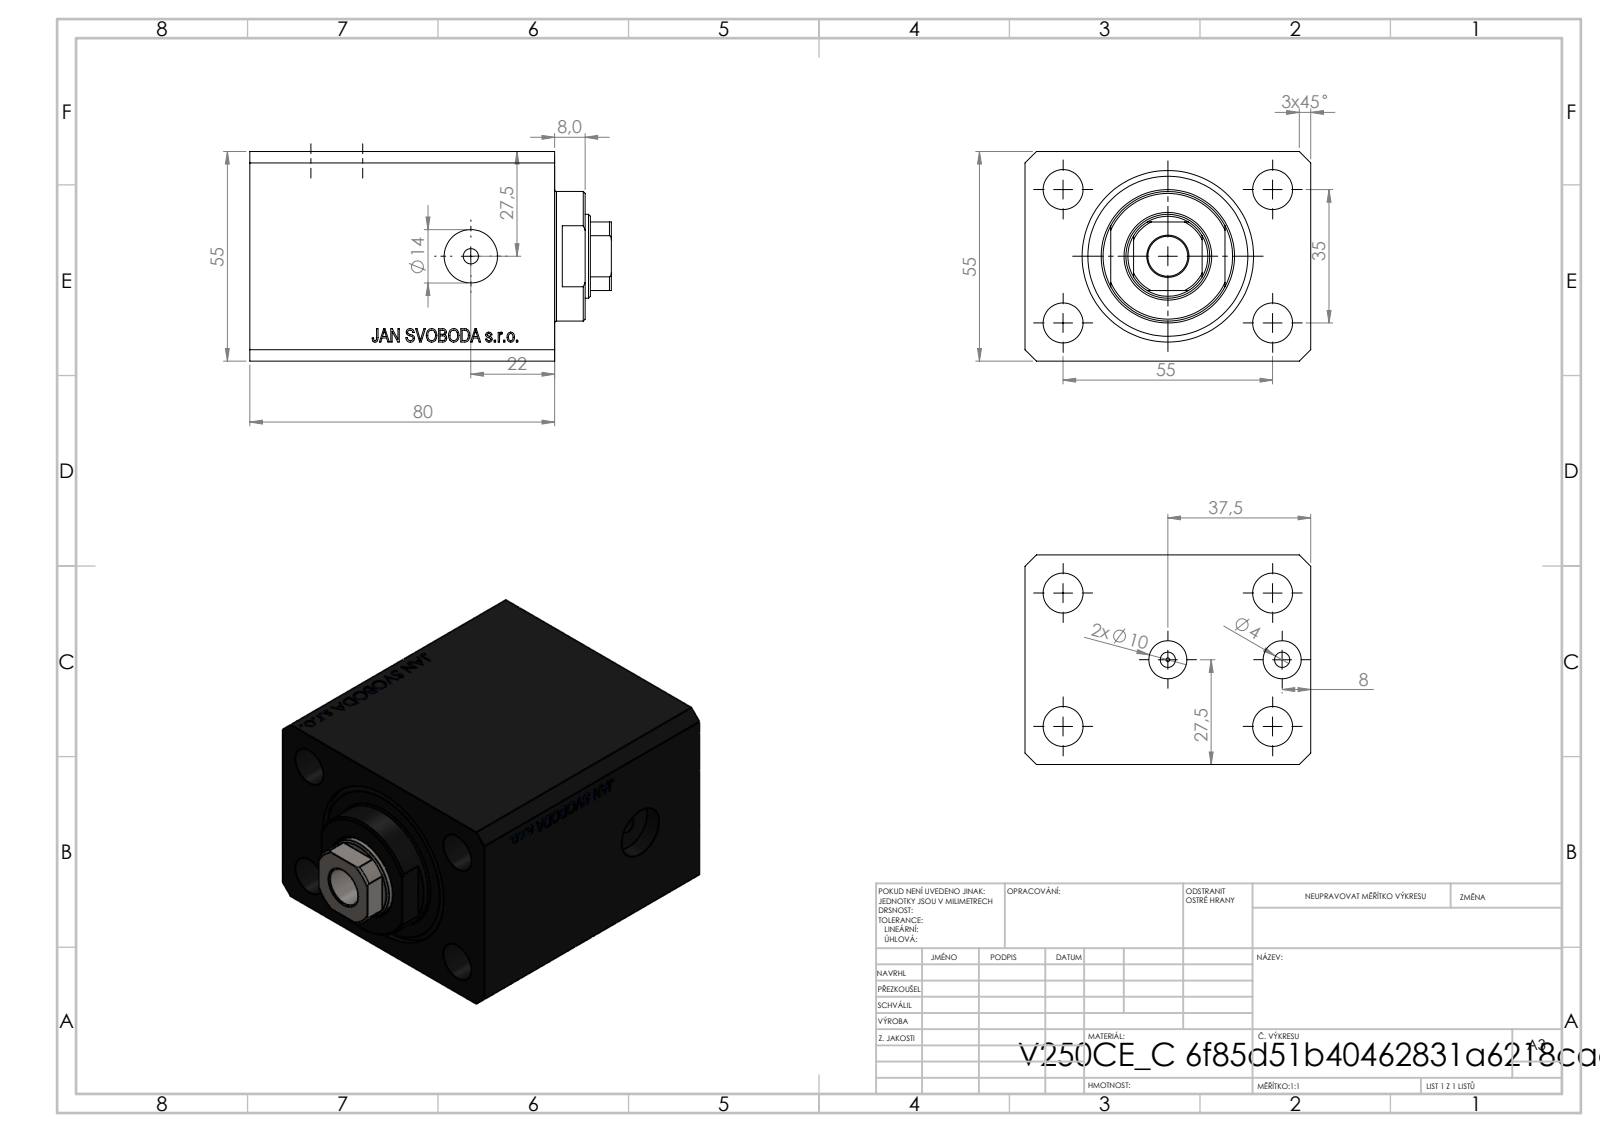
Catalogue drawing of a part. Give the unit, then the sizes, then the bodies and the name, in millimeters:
Units: millimetres
Overall size (bounding box): 95 × 75 × 55
Round holes (diameter × count): ⌀10.5 ×5, ⌀4 ×4, ⌀10 ×2, ⌀14 ×2, ⌀1.25 ×1, ⌀22 ×1, ⌀32 ×1, ⌀45 ×1
Round bosses / shafts (diameter × count): ⌀34 ×1
Partial cylindrical surfaces — rounded edges, fillets, slot ends (radius × count): R10.5 ×1
Main face-to-face distances: 55, 75, 80, 15, 65, 9.9, 55.1, 70.1, 87.66, 8
Hole centre spacings: 32.6, 17.68, 35, 55, 60.1, 65.19, 30, 36
Volume: 296 169 mm³ · Surface area: 64 654 mm²
Bodies: 3 solids, 872 faces (428 planar, 50 cylindrical, 394 other)
Part name (STEP PRODUCT): V250CE_C_Body; V250CE_VC_C; V250CE_C_VCP
STEP written by: SolidWorks 2019 (CONFIG_CONTROL_DESIGN)
